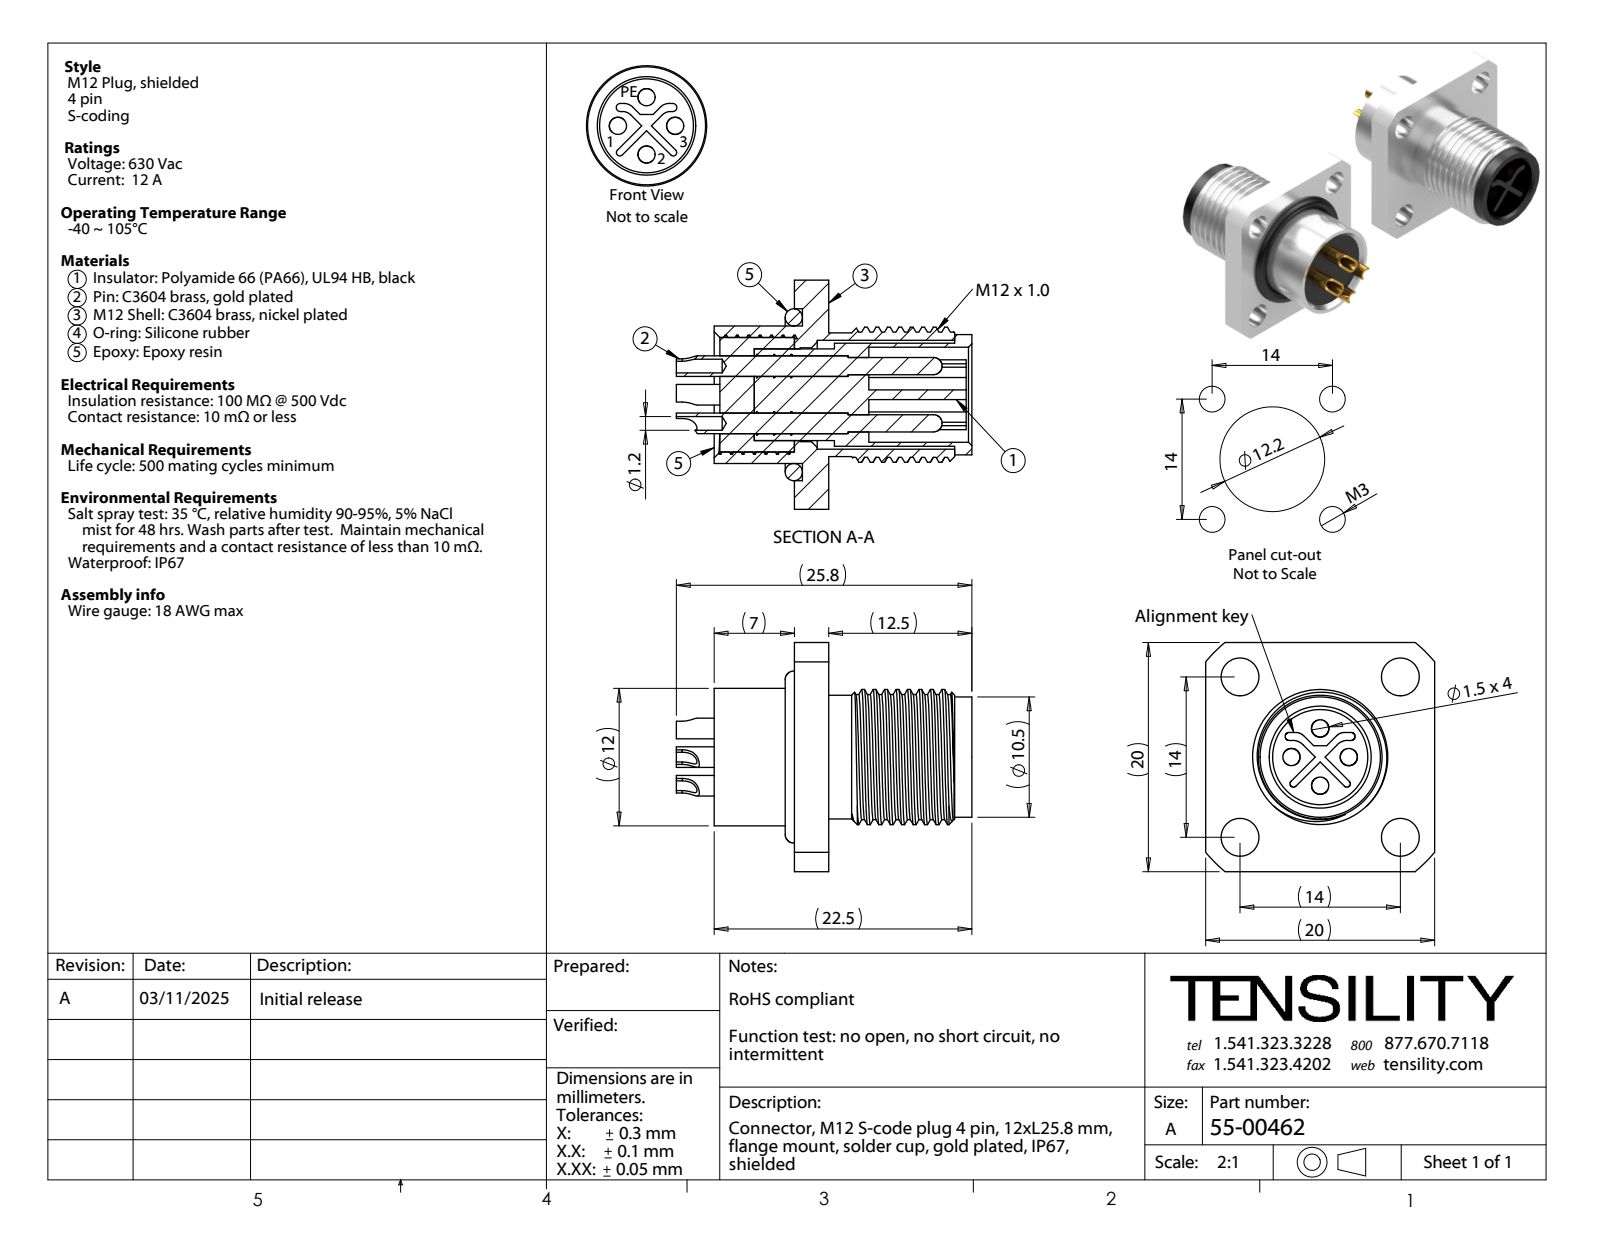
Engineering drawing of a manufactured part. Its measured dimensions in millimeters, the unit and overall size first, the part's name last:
Units: millimetres
Overall size (bounding box): 25.8 × 20 × 20
Round holes (diameter × count): ⌀1.2 ×4, ⌀1.5 ×4, ⌀3.3 ×4, ⌀8 ×1, ⌀8.2 ×1, ⌀8.3 ×1, ⌀9.5 ×1, ⌀10 ×1, ⌀15 ×1
Round bosses / shafts (diameter × count): ⌀1.8 ×4, ⌀12 ×1, ⌀11.8 ×1, ⌀10.92 ×1, ⌀10.8 ×1, ⌀10.5 ×1, ⌀9 ×1
Partial cylindrical surfaces — rounded edges, fillets, slot ends (radius × count): R0.3 ×2, R0.35 ×2, R1 ×2, R1.28 ×2, R1.7 ×2, R13 ×1
Main face-to-face distances: 3, 6.5, 3.5, 20, 10, 0.6, 2.3, 0.7, 9.5, 4.2
Hole centre spacings: 8.32, 11.8, 2.5, 3.54, 9.9, 14, 5, 19.8
Volume: 2 606 mm³ · Surface area: 5 139 mm²
Bodies: 8 solids, 314 faces (67 planar, 176 cylindrical, 71 other)
Part name (STEP PRODUCT): 55-00462-03L; 55-00462; 55-00462-02; 55-00462-01 (+2 more)
STEP written by: SolidWorks 2021 (CONFIG_CONTROL_DESIGN)
